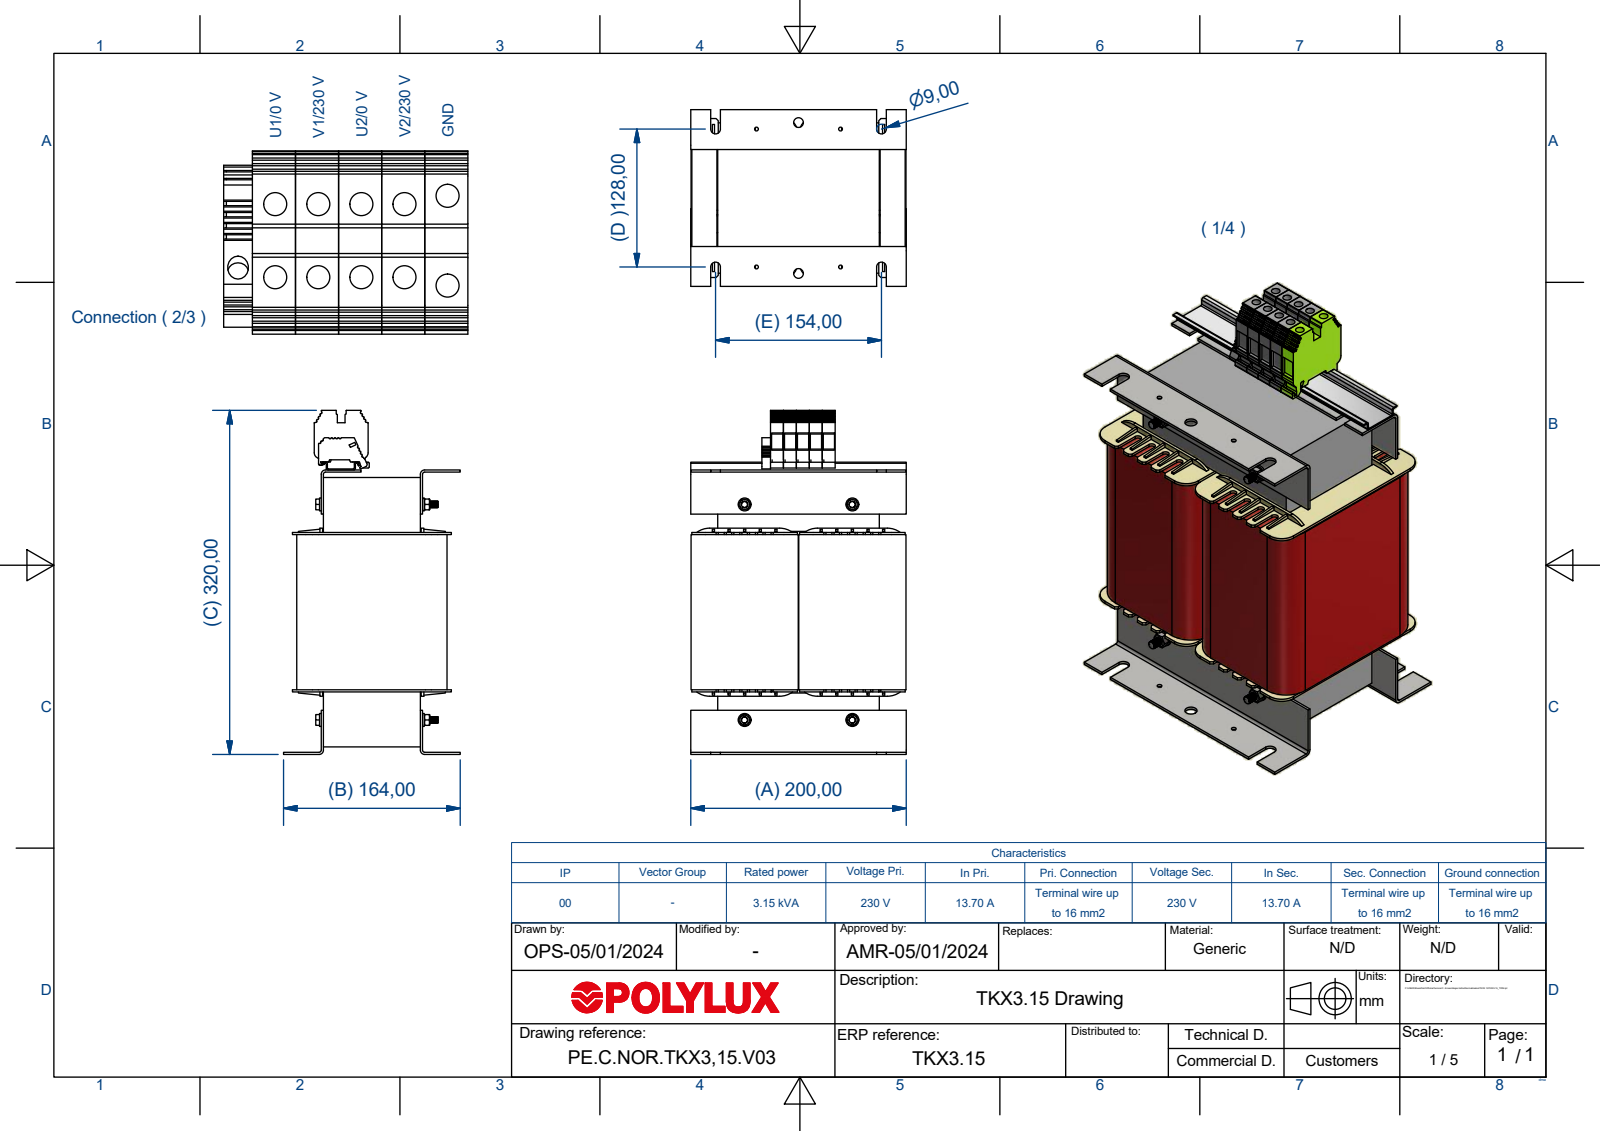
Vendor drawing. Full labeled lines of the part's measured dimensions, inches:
Part name (STEP PRODUCT): TKX3.15
STEP written by: Autodesk Inventor 2018 (AUTOMOTIVE_DESIGN)
Units: inches
Bodies: 0 solids, 1419 faces (1069 planar, 330 cylindrical, 20 other)
Overall size (bounding box): 12.571 × 7.874 × 6.457
Round holes (diameter × count): ⌀0.252 ×10, ⌀0.138 ×5, ⌀0.354 ×2, ⌀0.228 ×1
Round bosses / shafts (diameter × count): ⌀0.472 ×4, ⌀0.236 ×4
Partial cylindrical surfaces — rounded edges, fillets, slot ends (radius × count): R0.02 ×50, R0.108 ×16, R0.787 ×16, R0.039 ×11, R0.492 ×8, R0.079 ×6, R0.177 ×6, R0.008 ×5
Main face-to-face distances: 0.079, 0.974, 3.543, 0.945, 2.244, 2.323, 8.071, 7.992, 4.518, 0.03
Hole centre spacings: 0.472, 0.93, 0.801, 0.945, 1.239, 1.554, 5.494, 1.417
